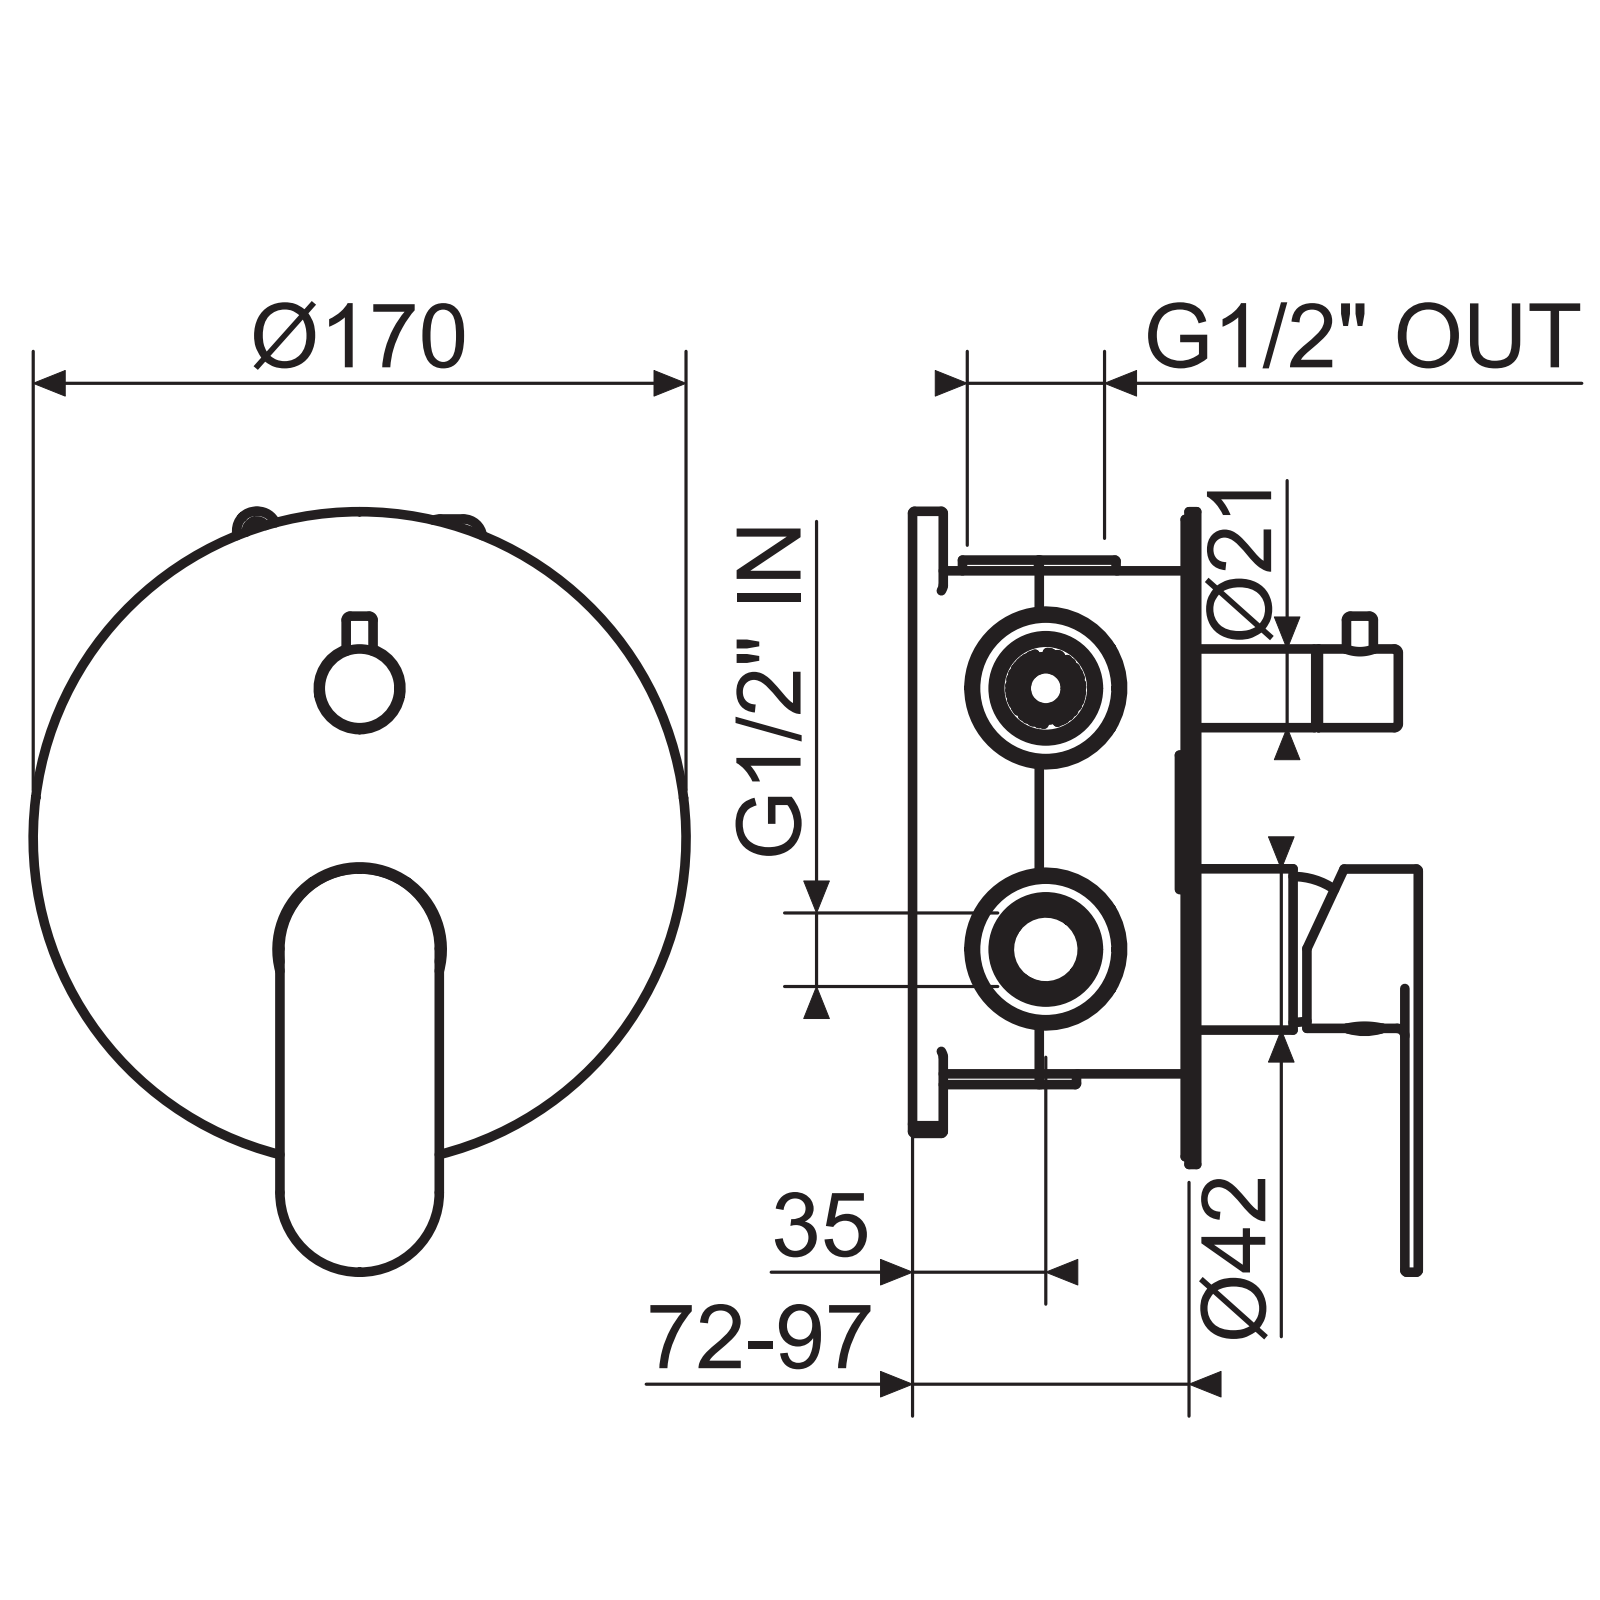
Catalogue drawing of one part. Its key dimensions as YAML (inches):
part_name: "SINMAC0008; SCCMAC0005; AUNO005C002; SPLMAC0004 (+8 more)"
step_written_by: "CREO PARAMETRIC BY PTC INC, 2020281 (CONFIG_CONTROL_DESIGN)"
units: inches
bodies: {solids: 11, faces: 420, planar: 94, cylindrical: 160, other: 166}
overall_size: [7.805, 6.693, 2.799]
volume: 4.69
surface_area: 130.4
round_holes:
  - {diameter: 0.039, count: 2}
  - {diameter: 0.165, count: 2}
  - {diameter: 0.315, count: 2}
  - {diameter: 0.201, count: 1}
  - {diameter: 0.205, count: 1}
  - {diameter: 0.217, count: 1}
  - {diameter: 0.256, count: 1}
  - {diameter: 0.295, count: 1}
  - {diameter: 0.472, count: 1}
  - {diameter: 0.551, count: 1}
  - {diameter: 0.709, count: 1}
  - {diameter: 0.846, count: 1}
round_bosses_or_shafts:
  - {diameter: 0.197, count: 2}
  - {diameter: 6.693, count: 1}
  - {diameter: 1.929, count: 1}
  - {diameter: 1.654, count: 1}
  - {diameter: 1.634, count: 1}
  - {diameter: 1.339, count: 1}
  - {diameter: 1.083, count: 1}
  - {diameter: 0.807, count: 1}
partial_cylinders:
  - {radius: 0.02, count: 27}
  - {radius: 0.039, count: 6}
  - {radius: 0.063, count: 6}
  - {radius: 0.059, count: 2}
  - {radius: 0.118, count: 2}
  - {radius: 0.148, count: 1}
  - {radius: 0.154, count: 1}
  - {radius: 0.817, count: 1}
face_to_face_distances: [0.079, 2.291, 2.37, 2.232, 0.138, 2.154, 0.157, 2.213, 1.146, 0.059]
hole_center_spacings: [0.224, 2.677]
